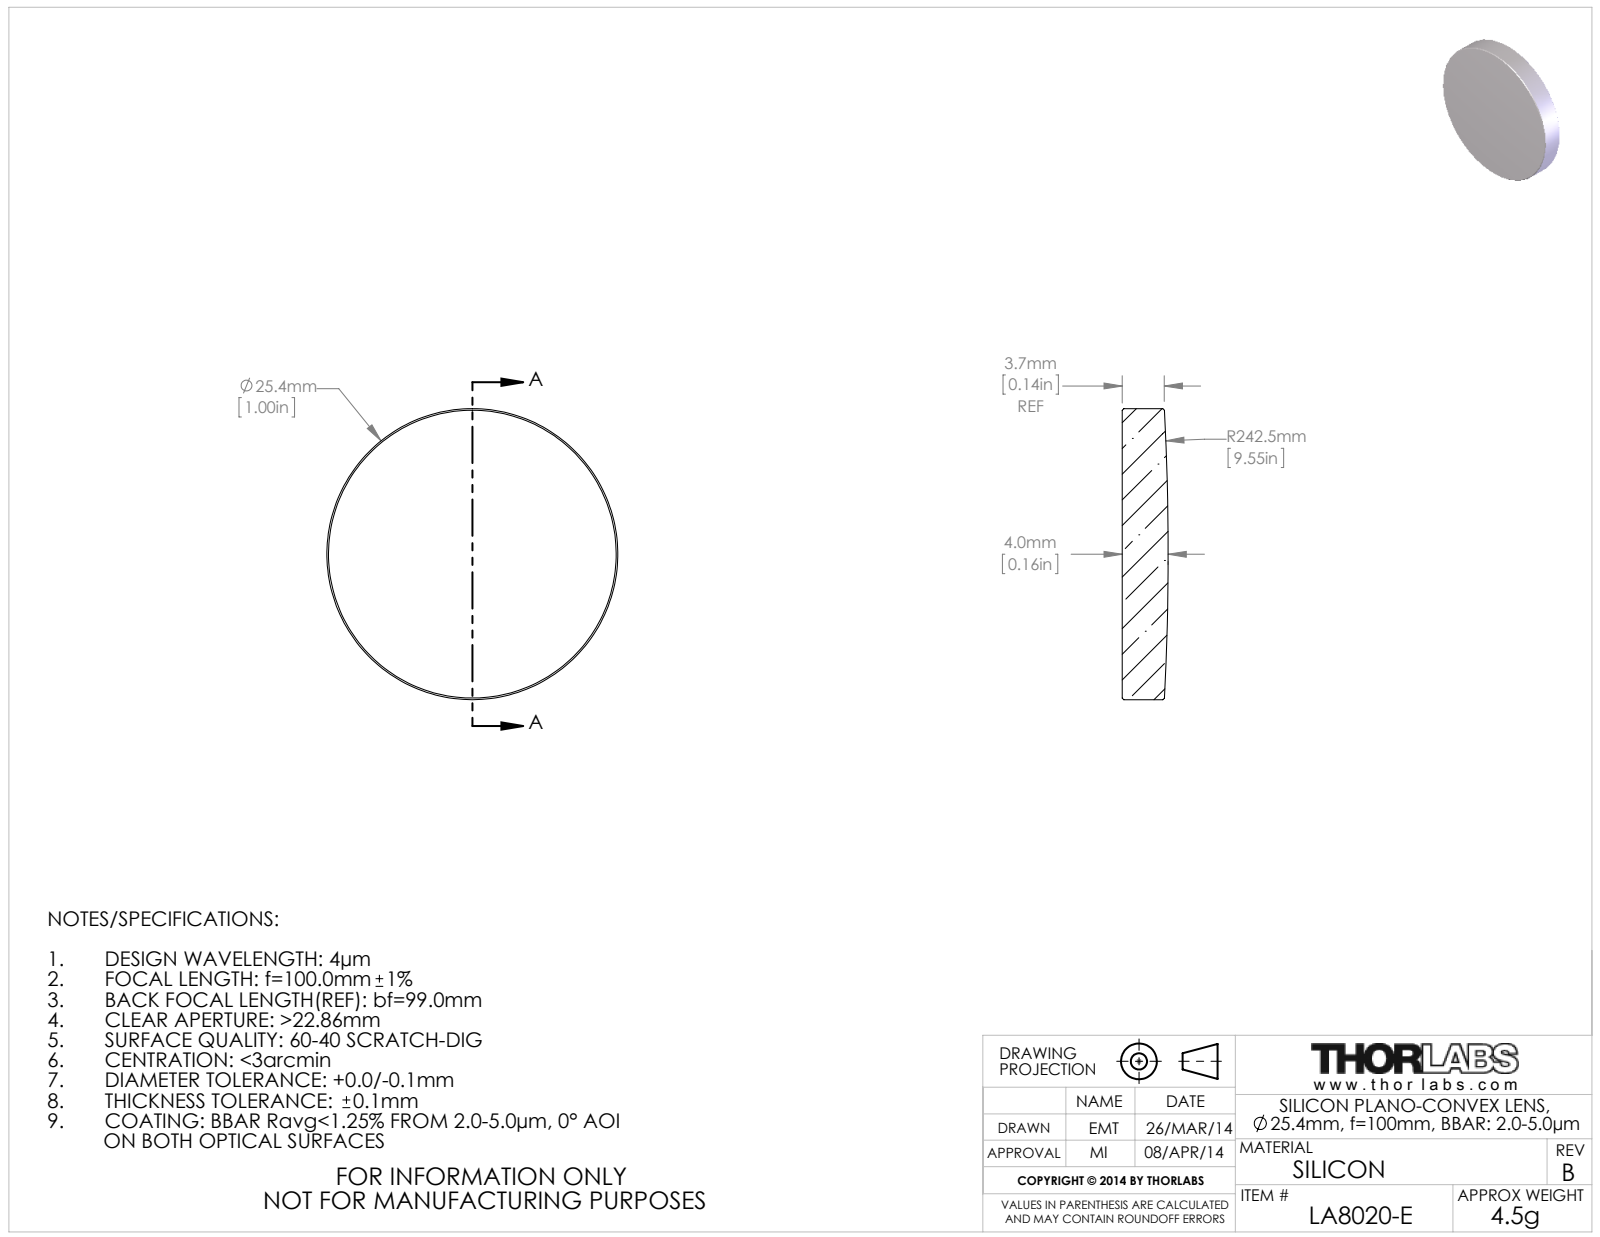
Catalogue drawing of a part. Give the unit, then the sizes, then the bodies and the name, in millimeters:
Units: millimetres
Overall size (bounding box): 25.4 × 25.4 × 4
Round bosses / shafts (diameter × count): ⌀25.4 ×1
Volume: 1 941 mm³ · Surface area: 1 294 mm²
Bodies: 1 solid, 9 faces (1 planar, 2 cylindrical, 6 other)
Part name (STEP PRODUCT): 20119-E0W
STEP written by: SolidWorks 2014 (CONFIG_CONTROL_DESIGN)
